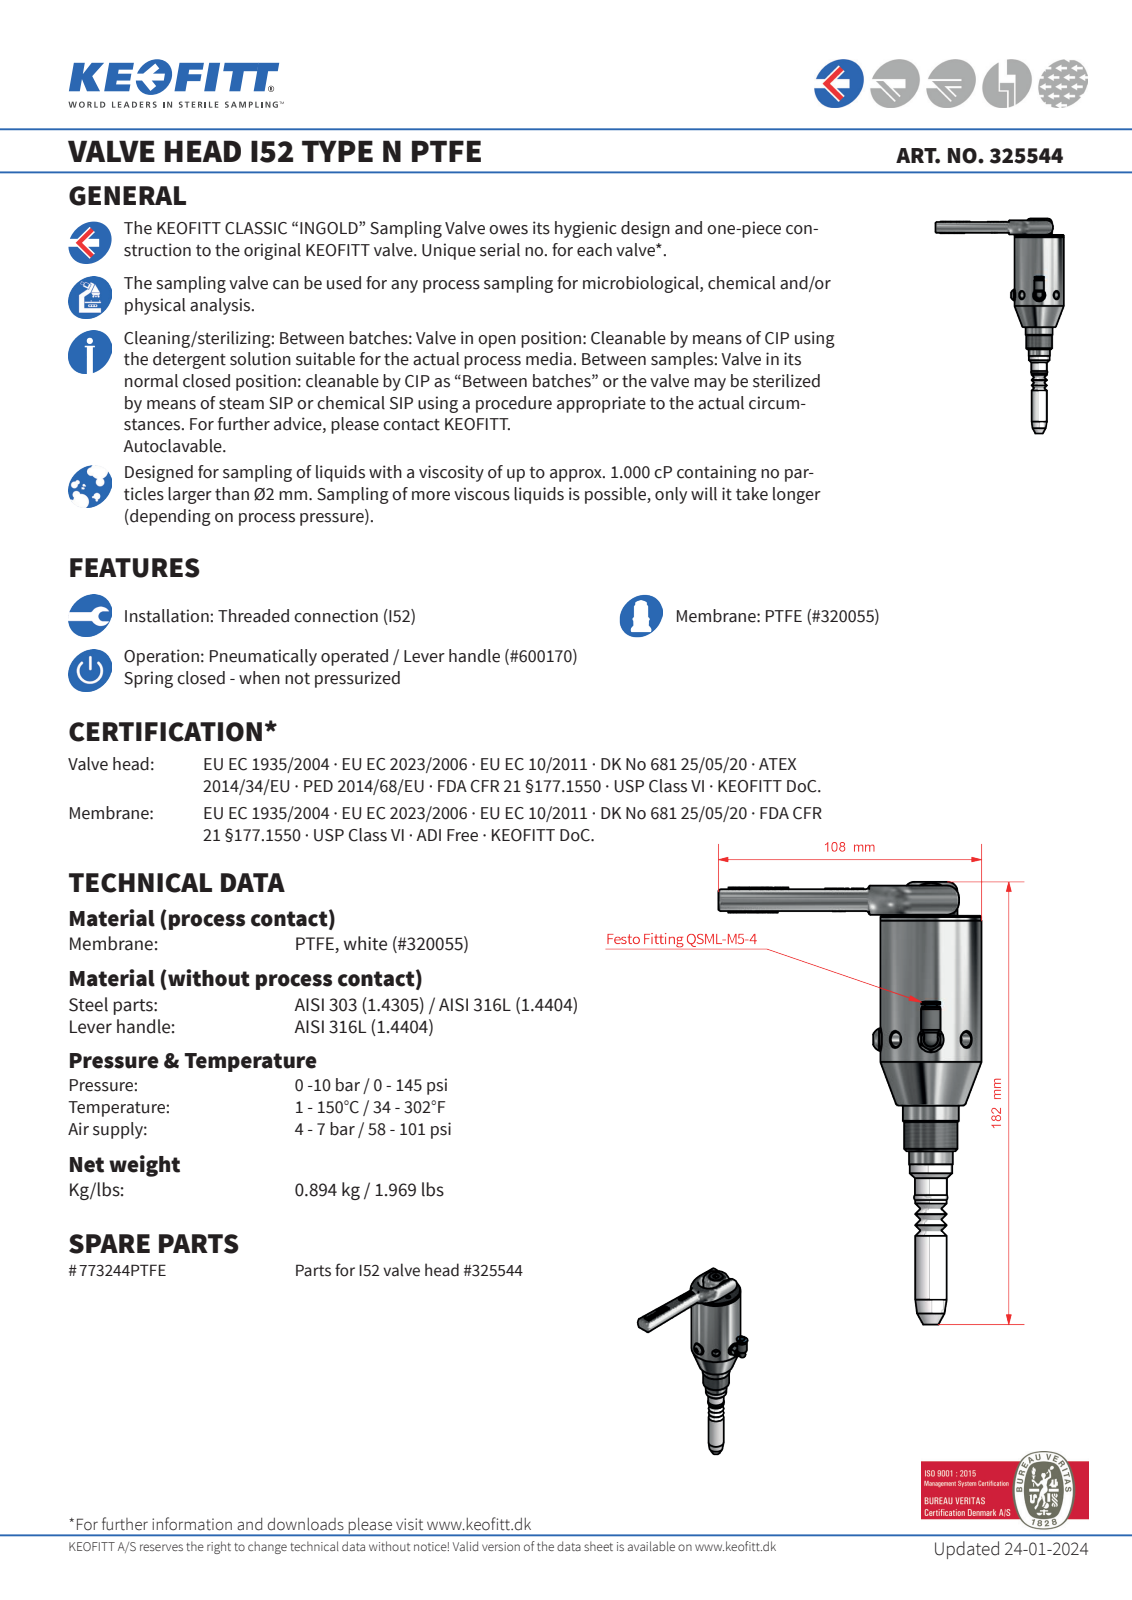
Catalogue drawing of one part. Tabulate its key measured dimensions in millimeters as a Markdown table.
| quantity | value |
| --- | --- |
| part name | 325544 |
| STEP written by | Autodesk Inventor 2022 (AUTOMOTIVE_DESIGN) |
| units | millimeters |
| bodies | 1 solid, 509 faces (214 planar, 66 cylindrical, 229 other) |
| overall size | 182.46 × 122.16 × 51.74 |
| volume | 131 980 mm³ |
| surface area | 23 116 mm² |
| round holes (diameter × count) | 4 × 1, 6 × 1 |
| round bosses / shafts (diameter × count) | 6.25 × 2, 5.6 × 2, 41.6 × 1, 41.5 × 1, 23 × 1, 22 × 1, 20.5 × 1, 18 × 1 |
| partial cylindrical surfaces (radius × count) | 0.5 × 14, 1 × 2, 1.5 × 2, 3.7 × 2, 3.9 × 2, 5 × 2, 3 × 1, 9.1 × 1 |
| main face-to-face distances | 1.5, 10.5, 9, 2, 12, 114.46, 3.1, 14.95, 102.46, 18.05 |
